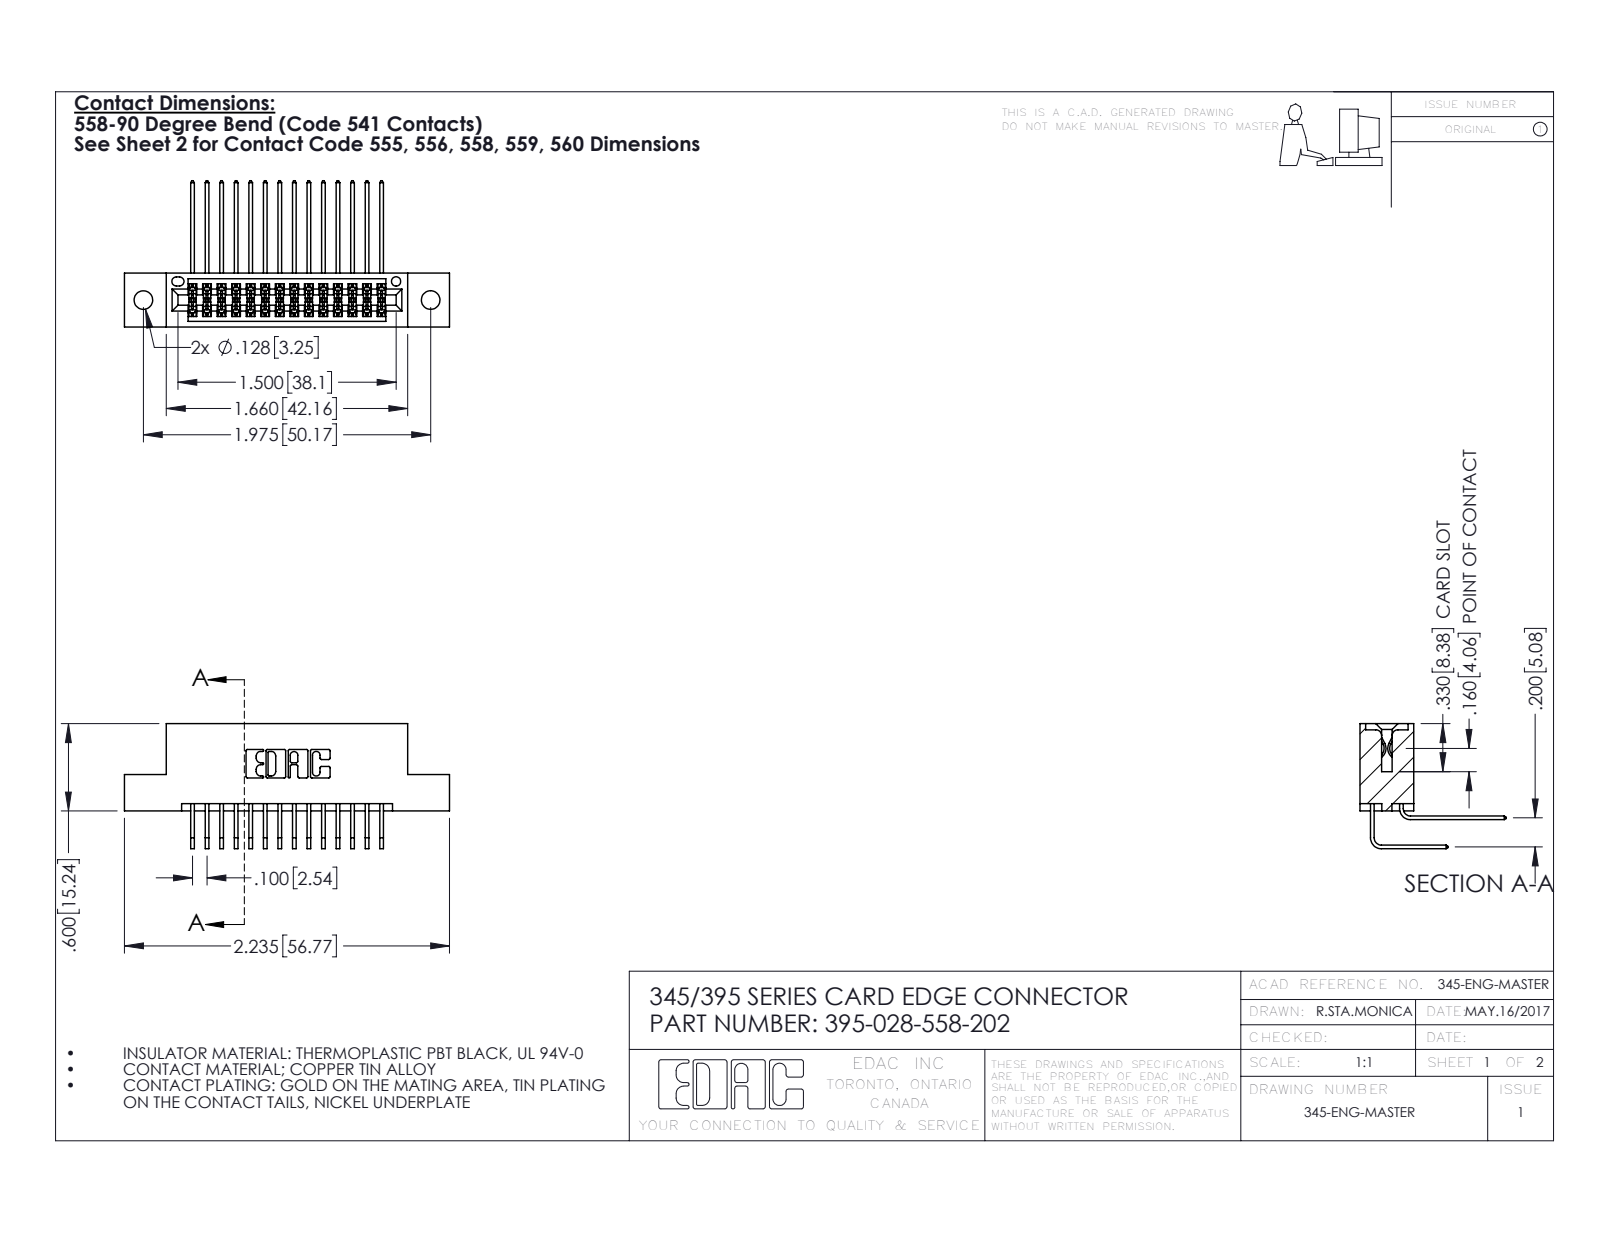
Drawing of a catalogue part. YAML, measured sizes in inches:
part_name: "395-028-558-202; 345 Part_Flush Mounting Lugs - 0.128 Dia; 345-292-001_558 Tail - 2; 345-292-001_558 559 Tail - 1"
step_written_by: "SolidWorks 2016 (CONFIG_CONTROL_DESIGN)"
units: inches
bodies: {solids: 29, faces: 1582, planar: 1060, cylindrical: 522, other: 0}
overall_size: [2.235, 1.005, 0.859]
volume: 0.328
surface_area: 12.24
round_holes:
  - {diameter: 0.128, count: 2}
  - {diameter: 0.064, count: 1}
partial_cylinders:
  - {radius: 0.006, count: 43}
  - {radius: 0.01, count: 22}
  - {radius: 0.007, count: 6}
  - {radius: 0.031, count: 6}
  - {radius: 0.026, count: 3}
  - {radius: 0.014, count: 2}
  - {radius: 0.019, count: 2}
  - {radius: 0.022, count: 2}
face_to_face_distances: [0.2, 0.072, 0.298, 0.37, 0.098, 0.272, 0.025, 0.225, 0.285, 0.1]
hole_center_spacings: [0.27, 1.742, 1.975]
